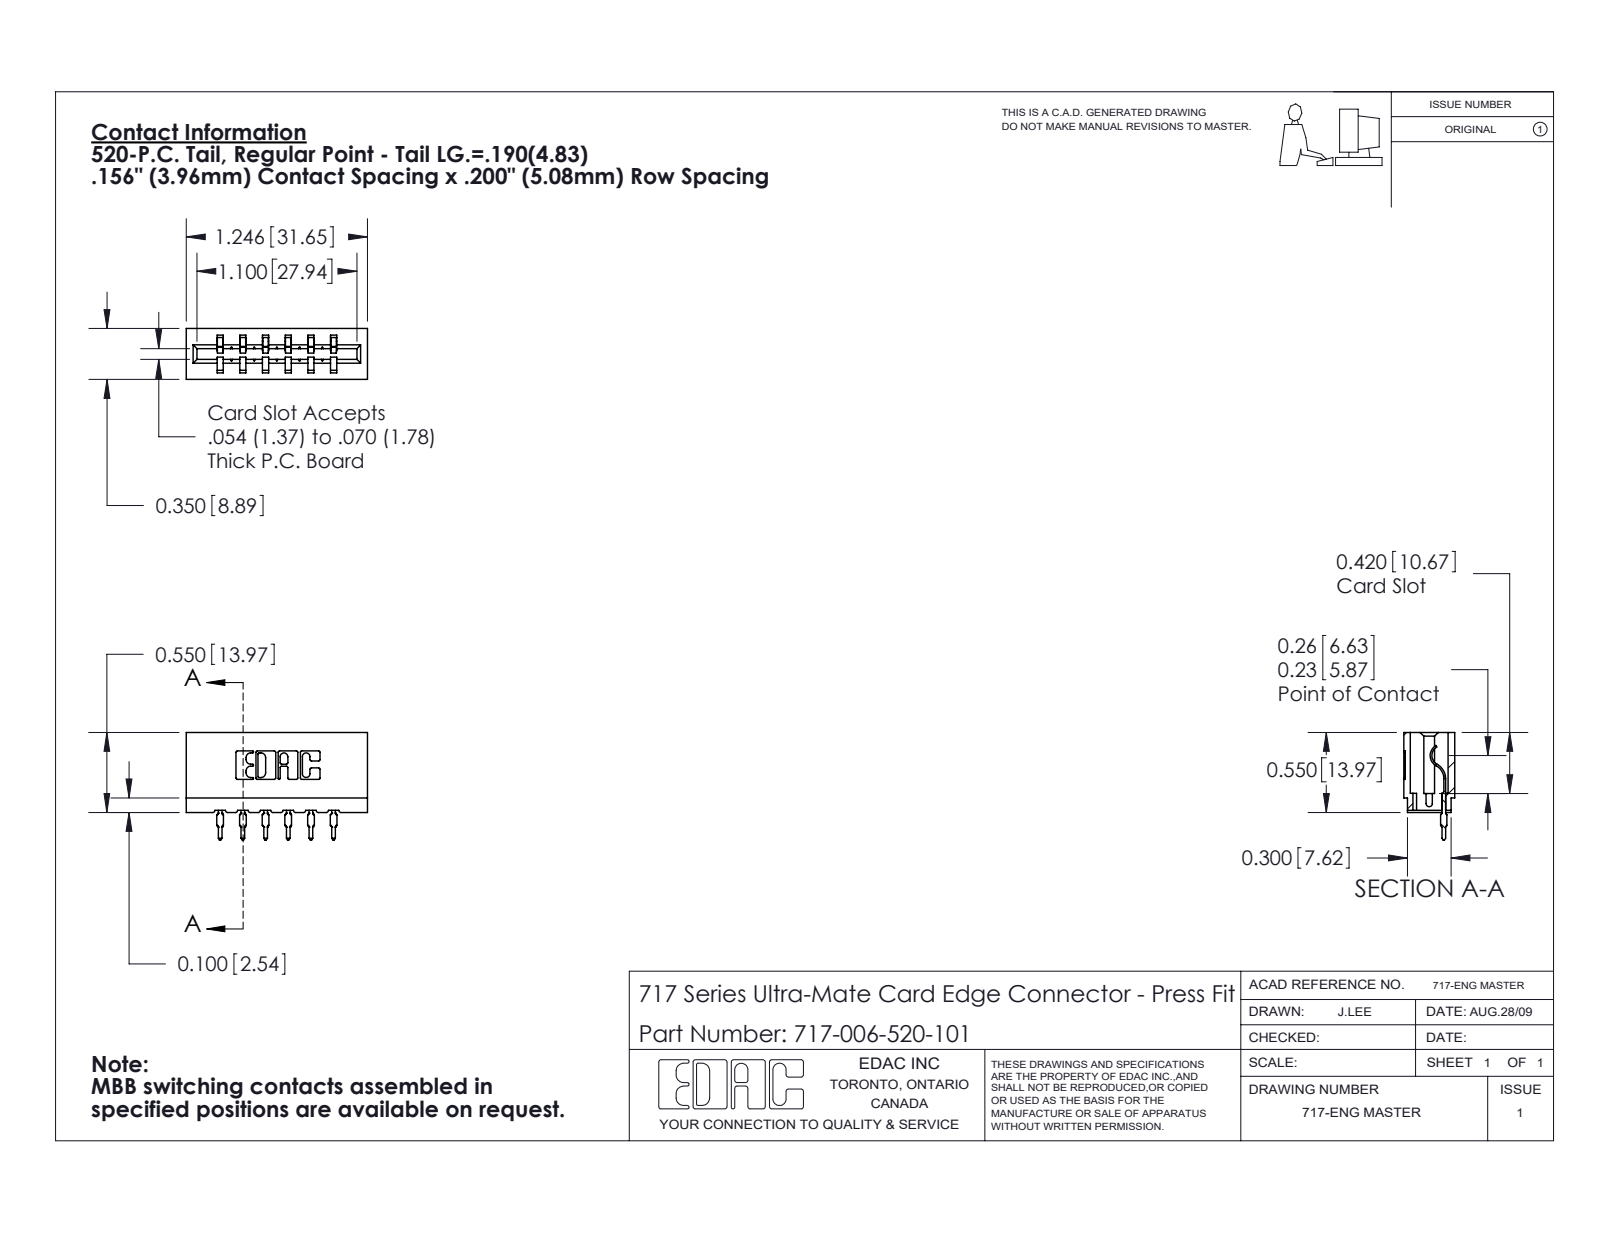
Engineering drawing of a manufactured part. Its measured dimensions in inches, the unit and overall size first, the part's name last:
Units: inches
Overall size (bounding box): 1.246 × 0.739 × 0.35
Partial cylindrical surfaces — rounded edges, fillets, slot ends (radius × count): R0.01 ×22, R0.015 ×12, R0.021 ×12, R0.007 ×6, R0.031 ×6, R0.005 ×4, R0.011 ×4, R0.026 ×3
Main face-to-face distances: 0.212, 0.156, 0.138, 0.35, 0.198, 0.312, 0.468, 0.312, 0.624, 0.042
Volume: 0.173 in³ · Surface area: 5.483 in²
Bodies: 7 solids, 772 faces (462 planar, 154 cylindrical, 156 other)
Part name (STEP PRODUCT): 717 Part_Insulator Option - 06; 717-006-520-101; 745-292-001_520
STEP written by: SolidWorks 2020 (CONFIG_CONTROL_DESIGN)
